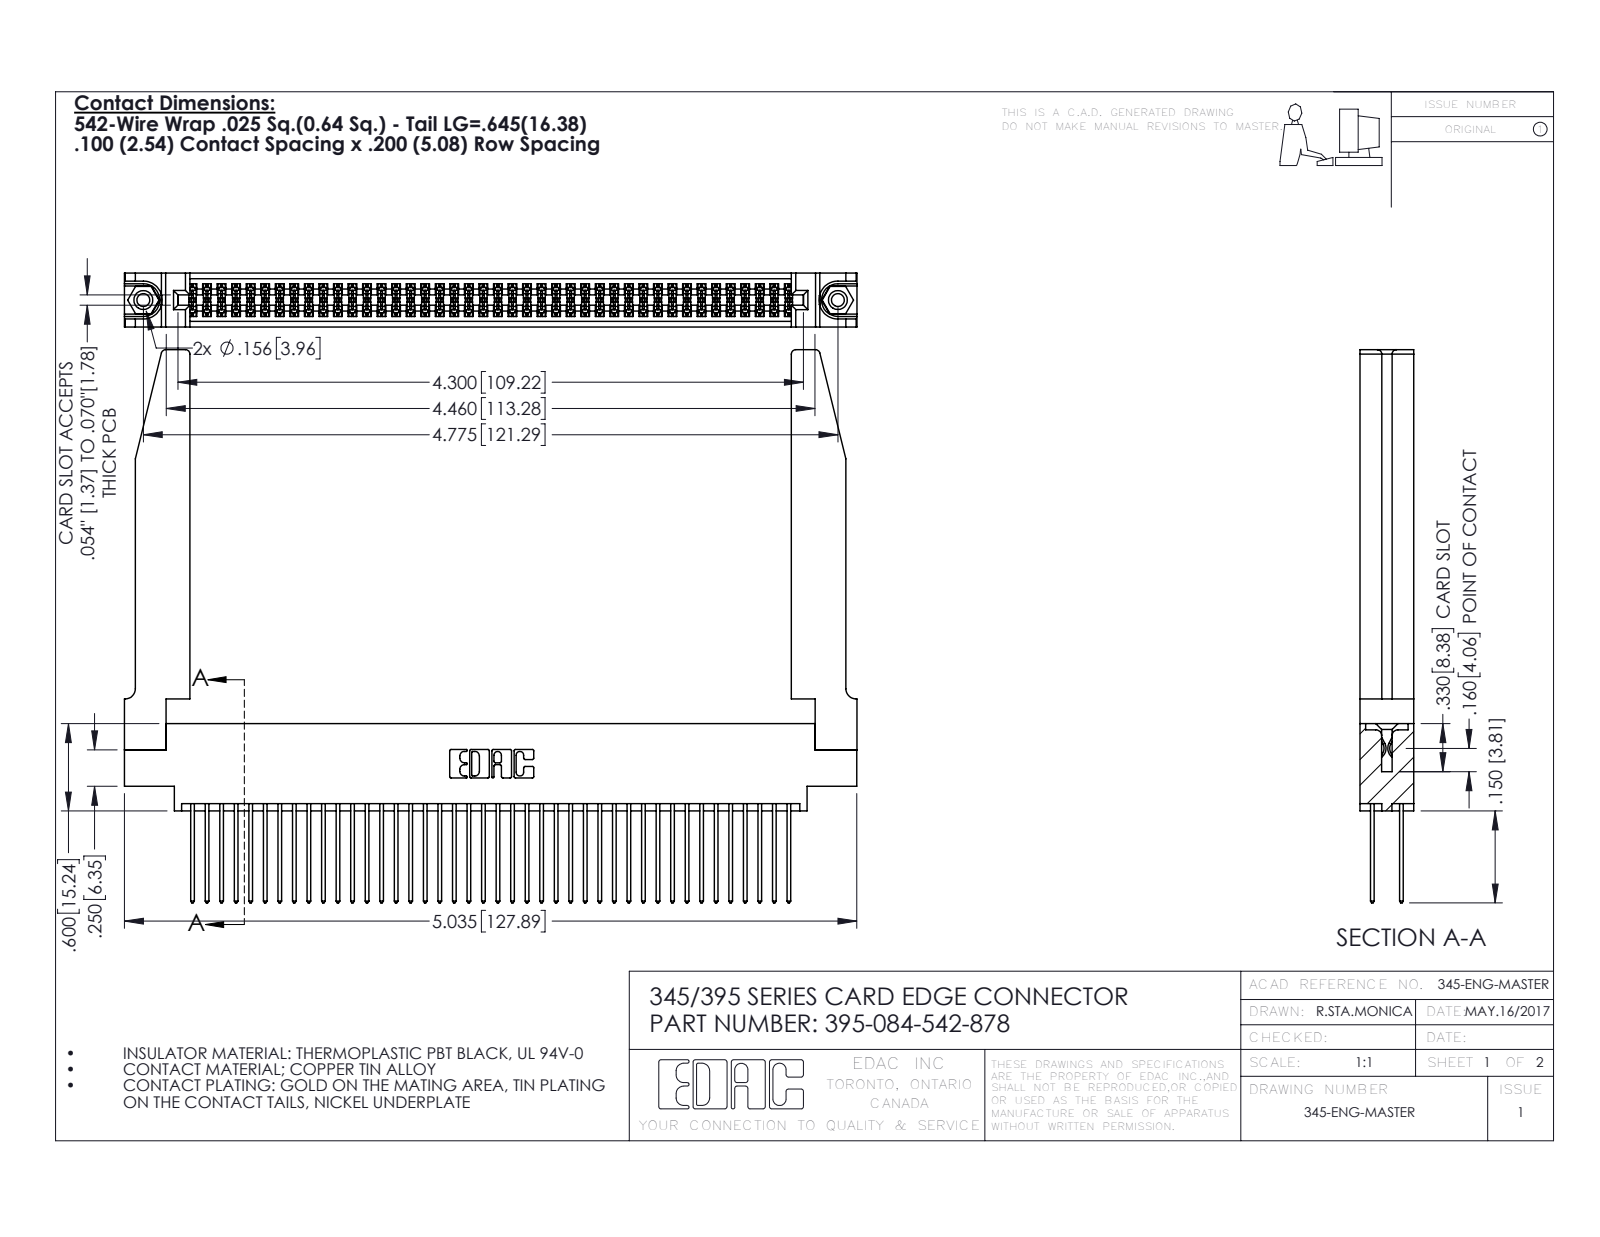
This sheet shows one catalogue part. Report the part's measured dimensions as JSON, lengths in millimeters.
{"part_name": "345-292-001_345-293-142; 345-220-078_345-220-078; 345 Part_0.170 Offset - 0.156 Dia-TH; 345-250-001_345-250-001-102 (+1 more)", "step_written_by": "SolidWorks 2016 (CONFIG_CONTROL_DESIGN)", "units": "millimeters", "bodies": {"solids": 89, "faces": 4564, "planar": 2998, "cylindrical": 1514, "other": 52}, "overall_size": [127.9, 96.6, 9.4], "volume_mm3": 20470, "surface_area_mm2": 27590, "round_holes": [[2.3, 2], [3.2, 2], [4, 2], [1.6, 1]], "round_bosses_or_shafts": [[3.9, 2]], "partial_cylinders_radius": [[0.2, 126], [0.3, 84], [0.3, 22], [0.8, 8], [0.2, 6], [0.8, 6], [0.7, 3], [0.4, 2]], "face_to_face_distances": [1.8, 7.6, 9.4, 2.5, 6.9, 0.6, 5.1, 5.7, 4.4, 3.8], "hole_center_spacings": [6.9, 115.3, 121.3]}
